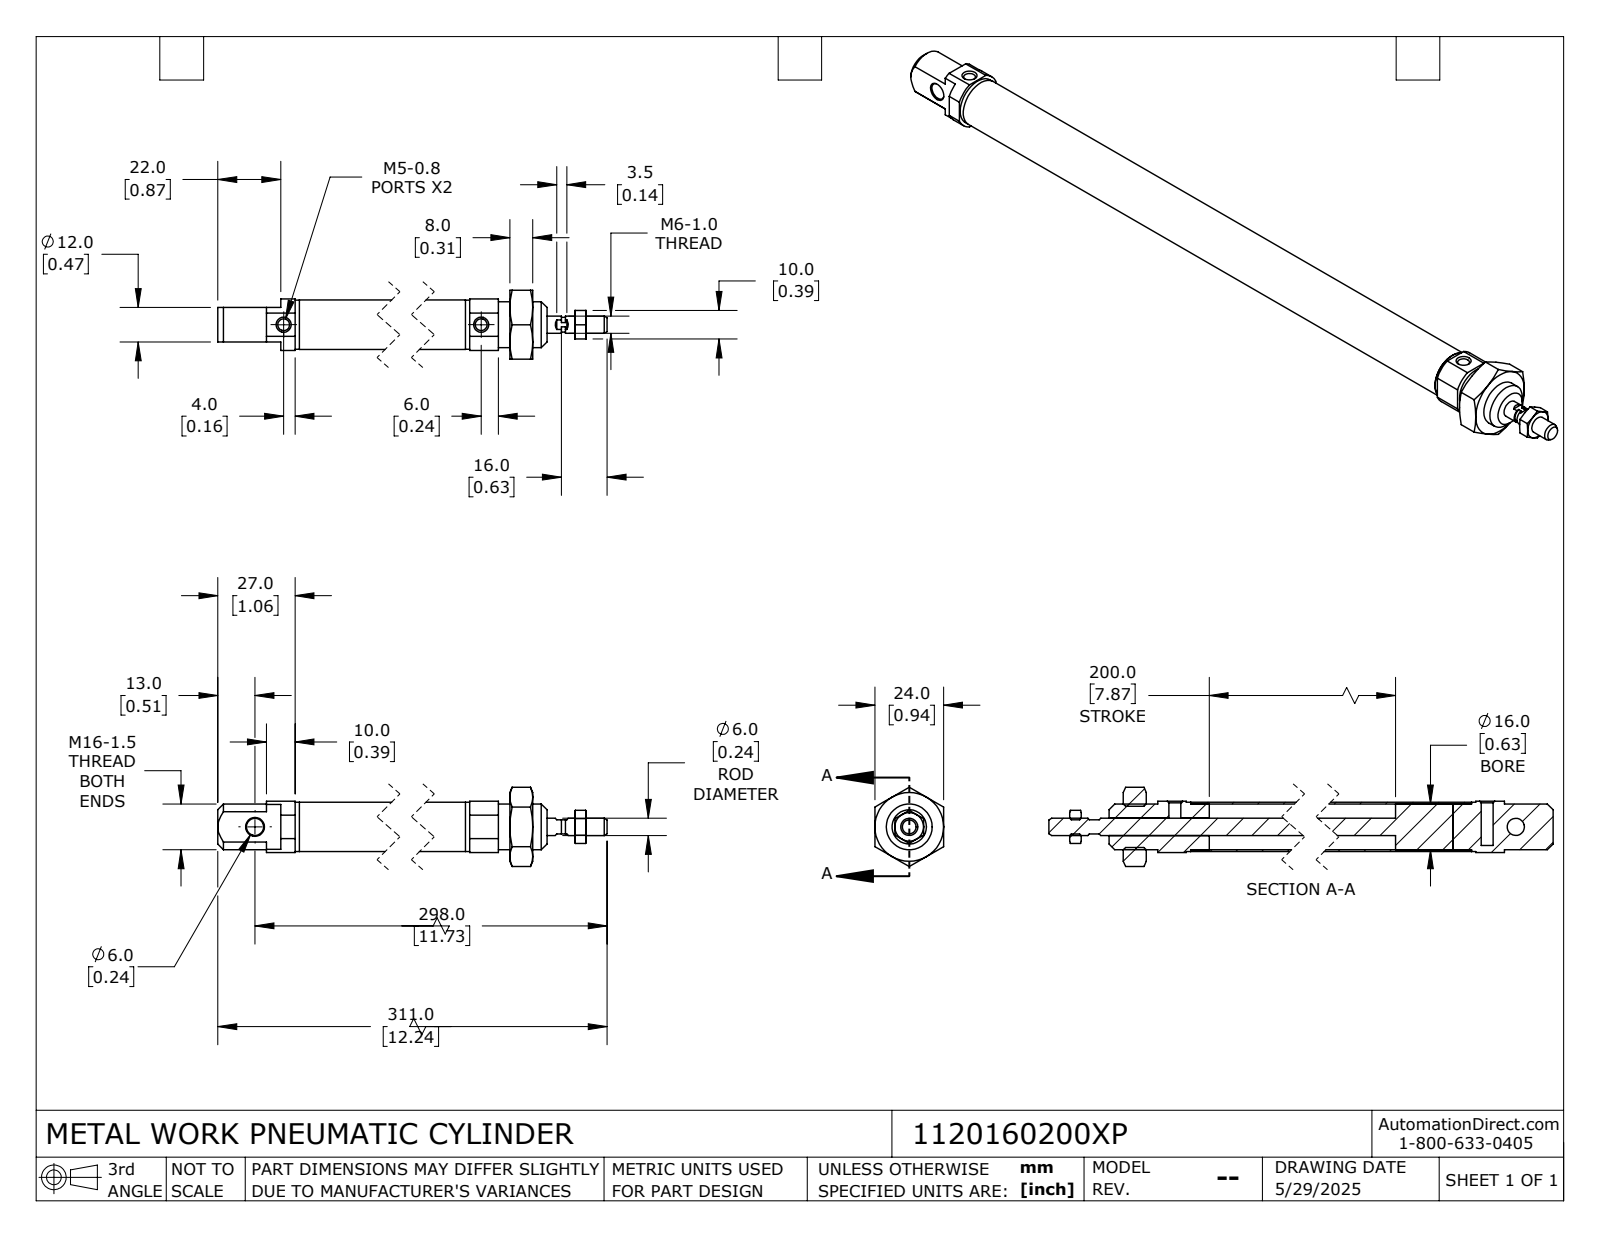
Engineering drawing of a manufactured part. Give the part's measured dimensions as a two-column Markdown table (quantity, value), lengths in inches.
| quantity | value |
| --- | --- |
| part name | 1120160200XP_ROD; 1120160200XP_BODY; 1120160200XP |
| STEP written by | SolidWorks 2024 (CONFIG_CONTROL_DESIGN) |
| units | inches |
| bodies | 6 solids, 146 faces (55 planar, 45 cylindrical, 46 other) |
| overall size | 12.244 × 1.091 × 0.945 |
| volume | 2.145 in³ |
| surface area | 59.42 in² |
| round holes (diameter × count) | 0.163 × 2, 0.194 × 1, 0.236 × 1, 0.566 × 1 |
| round bosses / shafts (diameter × count) | 0.68 × 1, 0.677 × 1, 0.636 × 1, 0.63 × 1, 0.236 × 1, 0.205 × 1 |
| partial cylindrical surfaces (radius × count) | 0.388 × 1 |
| main face-to-face distances | 0.315, 0.709, 0.945, 0.866, 9.843, 0.472, 10.039, 0.669, 9.528, 0.117 |
| hole center spacings | 9.606 |
